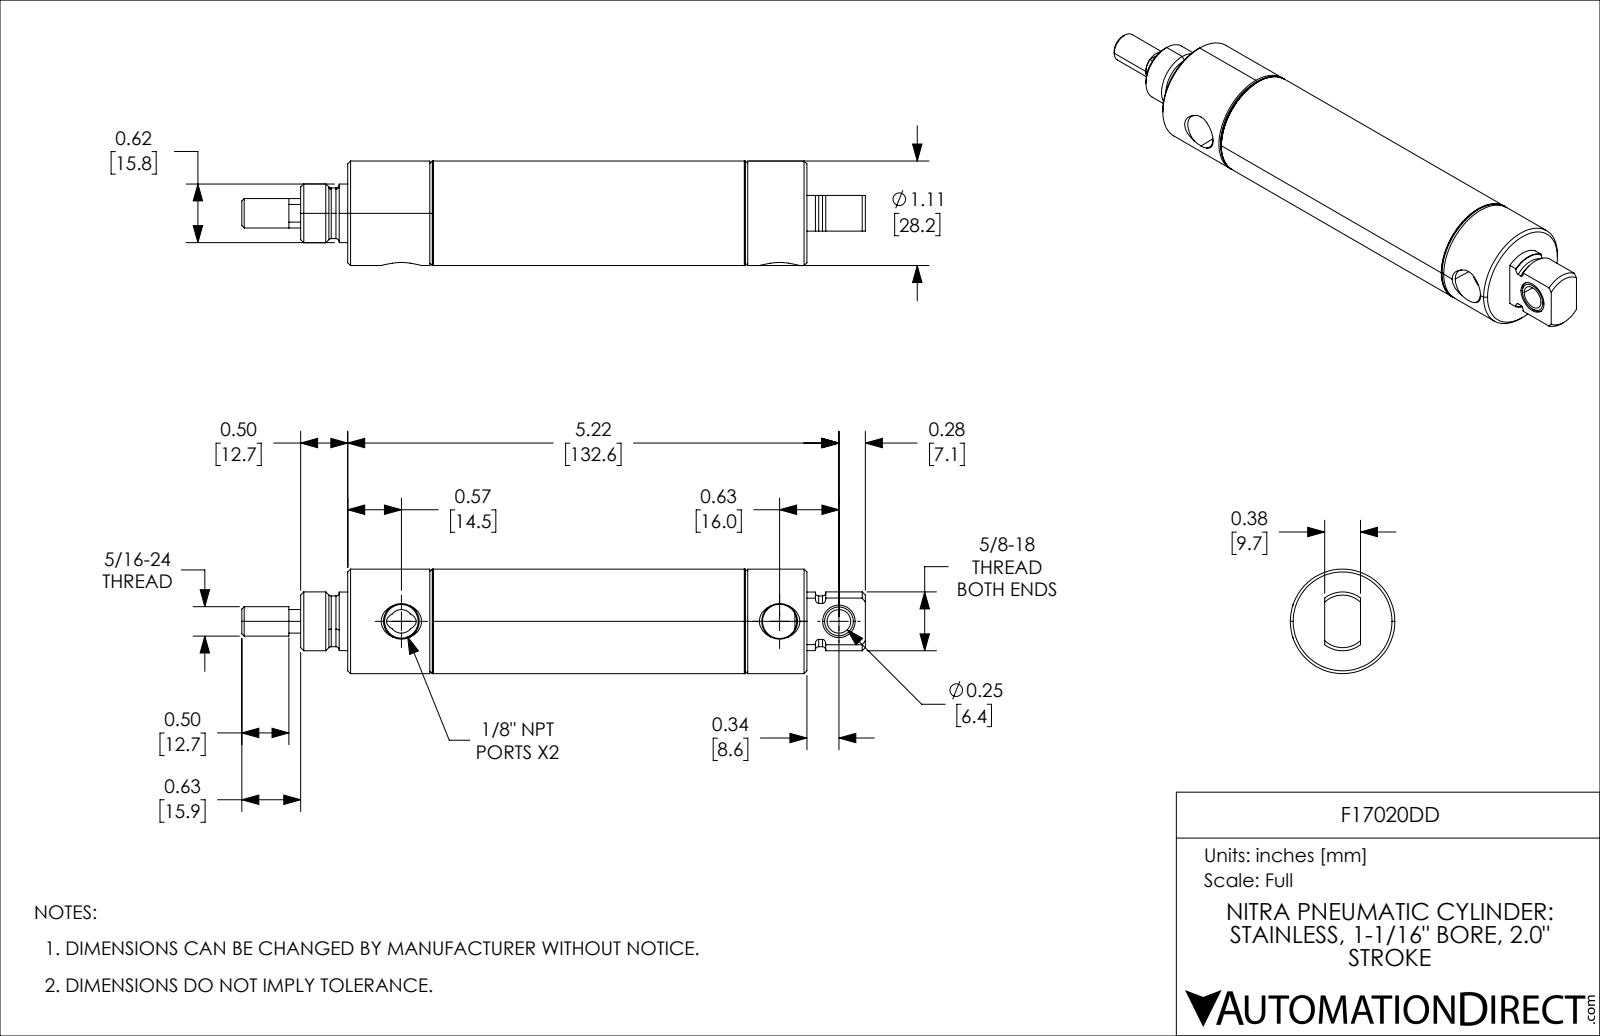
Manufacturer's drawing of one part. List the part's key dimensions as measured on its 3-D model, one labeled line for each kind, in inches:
Part name (STEP PRODUCT): F17020DD_5; F17020DD_11; F17020DD_7; F17020DD_9 (+2 more)
STEP written by: SolidWorks 2021 (CONFIG_CONTROL_DESIGN)
Units: inches
Bodies: 5 solids, 156 faces (30 planar, 58 cylindrical, 68 other)
Overall size (bounding box): 6.625 × 1.11 × 1.11
Volume: 3.081 in³ · Surface area: 49.99 in²
Round holes (diameter × count): ⌀0.251 ×1, ⌀0.336 ×1, ⌀0.346 ×1, ⌀0.364 ×1, ⌀0.375 ×1, ⌀0.75 ×1, ⌀1.012 ×1
Round bosses / shafts (diameter × count): ⌀1.11 ×1, ⌀1.072 ×1, ⌀0.625 ×1, ⌀0.622 ×1, ⌀0.539 ×1, ⌀0.313 ×1, ⌀0.312 ×1
Partial cylindrical surfaces — rounded edges, fillets, slot ends (radius × count): R0.125 ×1, R0.269 ×1
Main face-to-face distances: 0.875, 2, 2.875, 3.754, 1.754, 0.879, 1.125, 3.125, 4, 4.879
Hole centre spacings: 0.63
